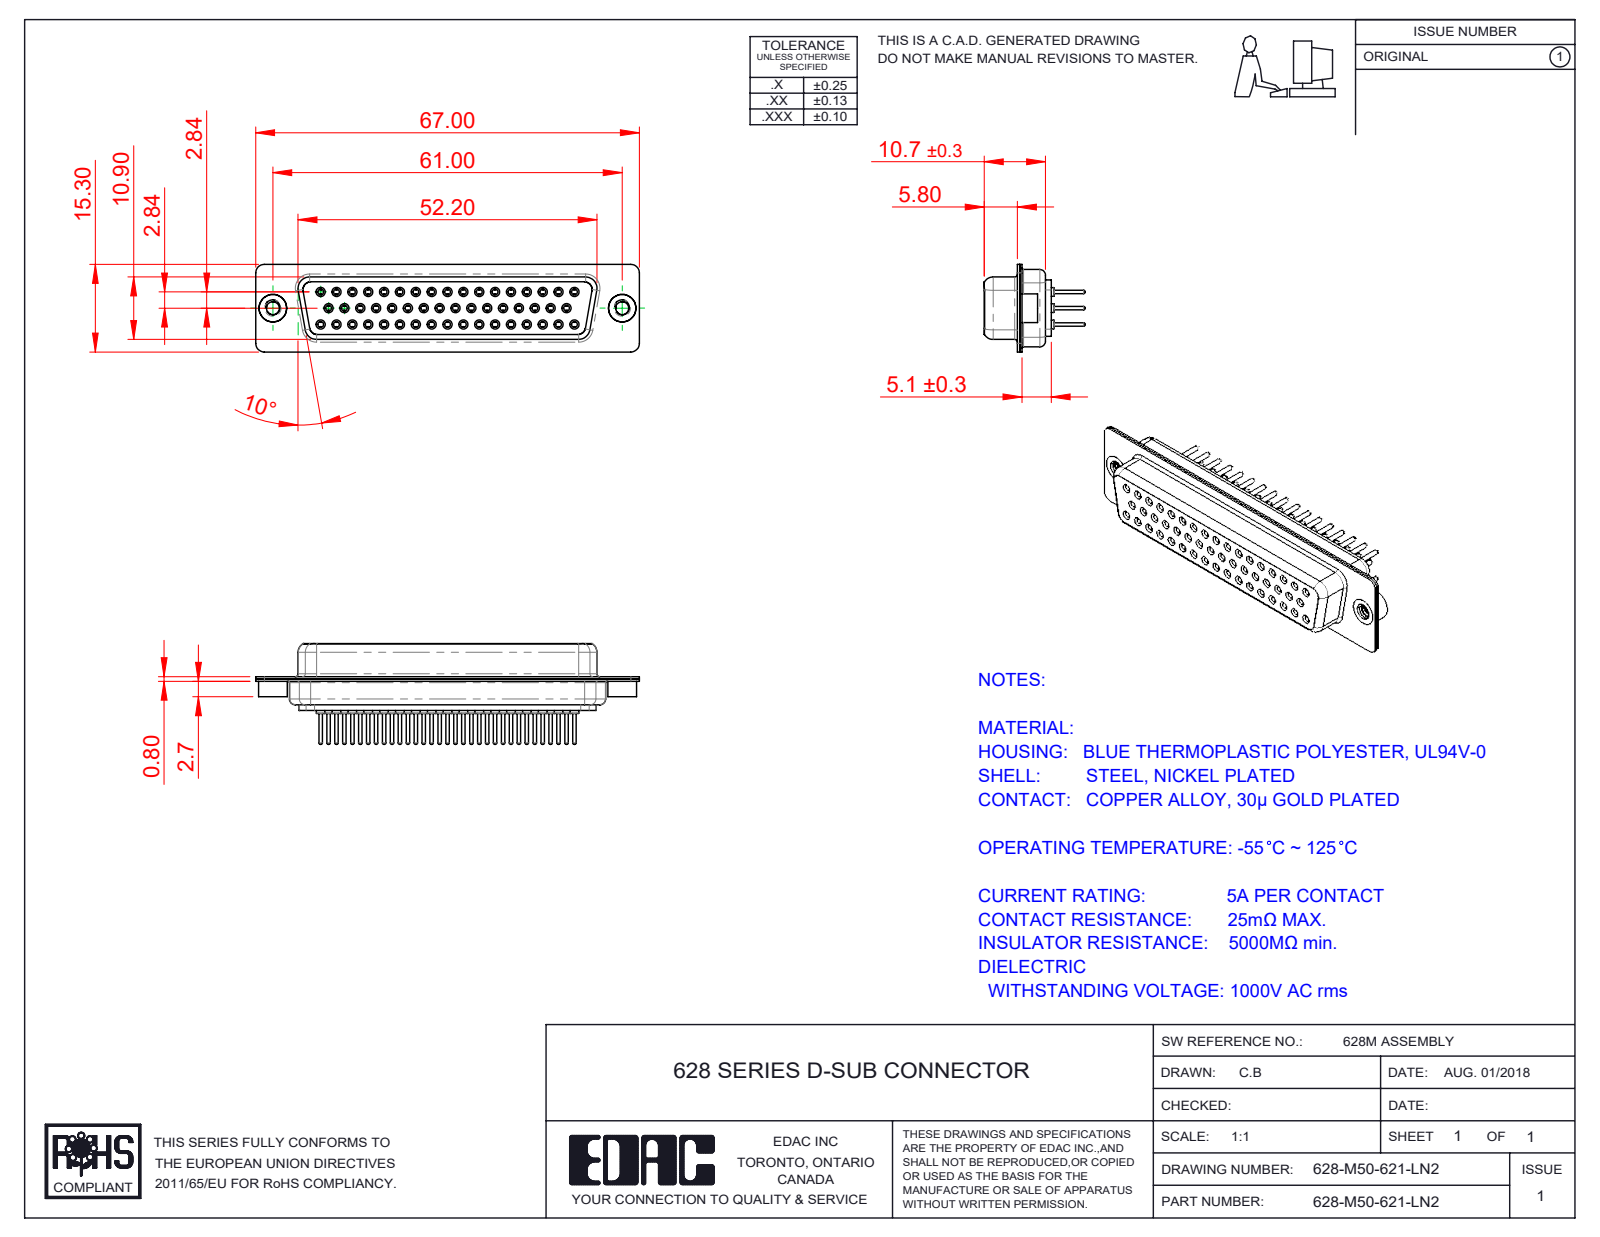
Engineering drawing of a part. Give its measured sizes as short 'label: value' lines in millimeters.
name: 628M Shell Front_50 Contacts; 628M Housing_50 Contacts; 628M Shell Rear_50 Contacts; 628-M50-621-LN2 (+4 more)
written by: SolidWorks 2020 (CONFIG_CONTROL_DESIGN)
unit: mm
bodies: 55 solids, 3029 faces (817 planar, 1087 cylindrical, 1125 other)
size: 67 × 17.6 × 15.3
volume: 6 623 mm³; area: 15 043 mm²
holes: 50× ⌀1, 50× ⌀1.1, 50× ⌀1.7, 50× ⌀1.8, 50× ⌀2, 2× ⌀2.26, 2× ⌀4, 2× ⌀4.8
bosses: 50× ⌀2.2, 50× ⌀1.6, 50× ⌀1.5, 50× ⌀0.6, 2× ⌀5, 2× ⌀4.9
rounds: 16× R1.5, 12× R2, 8× R1.35, 8× R1.6, 4× R0.25, 4× R0.5, 4× R0.6, 4× R0.65
face distances: 0.4, 1.3, 11.8, 0.9, 5.5, 5.9, 0.85, 13.1, 5.8, 10.05
hole spacings: 3.16, 2.77, 5.54, 8.31, 11.08, 13.85, 16.62, 19.39
